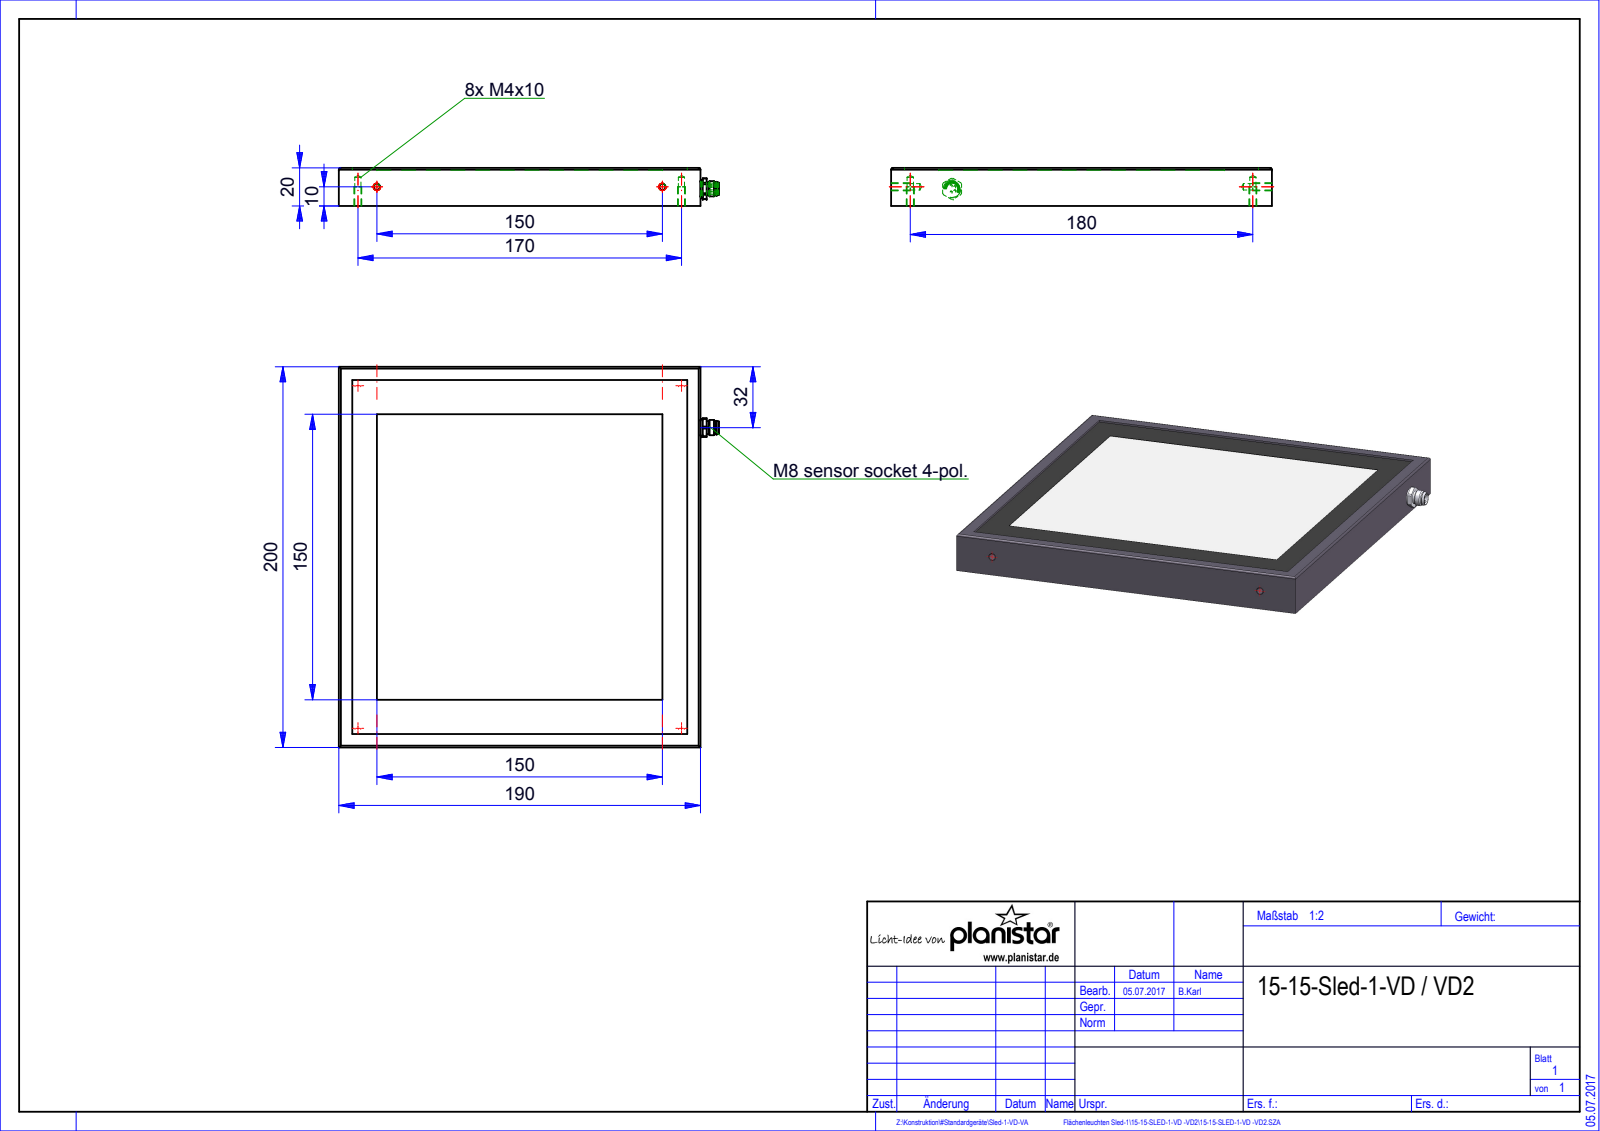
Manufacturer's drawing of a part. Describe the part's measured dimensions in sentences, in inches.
The part is named "Root; Baugruppe_Xled-2-VD; QUADER_0; 09-3391-00-04". Its 3-D file was written by "HiCAD 2015 2002.1 Build 408 (AUTOMOTIVE_DESIGN)". It is 2 solids with 90 faces: 36 planar, 37 cylindrical and 17 other. Overall it measures 7.874 by 7.862 by 0.787 inches. Its volume is 44.04 cubic inches and its surface area 146 square inches. Round holes: 6 of diameter 0.13, 6 of diameter 0.157, 1 of diameter 0.228. Round bosses or shafts: 4 of diameter 0.039, 1 of diameter 0.315, 1 of diameter 0.283, 1 of diameter 0.268, 1 of diameter 0.252. Partial cylindrical surfaces (rounded edges, fillets, slot ends): 4 of radius 0.039, 1 of radius 0.217. The main face-to-face distances are 0.74, 0.748, 0.787, 0.047, 0.039, 7.48, 7.874, 0.276, 7.205, 7.598. The hole center spacings are 6.693, 7.087, 9.748, 5.906.
